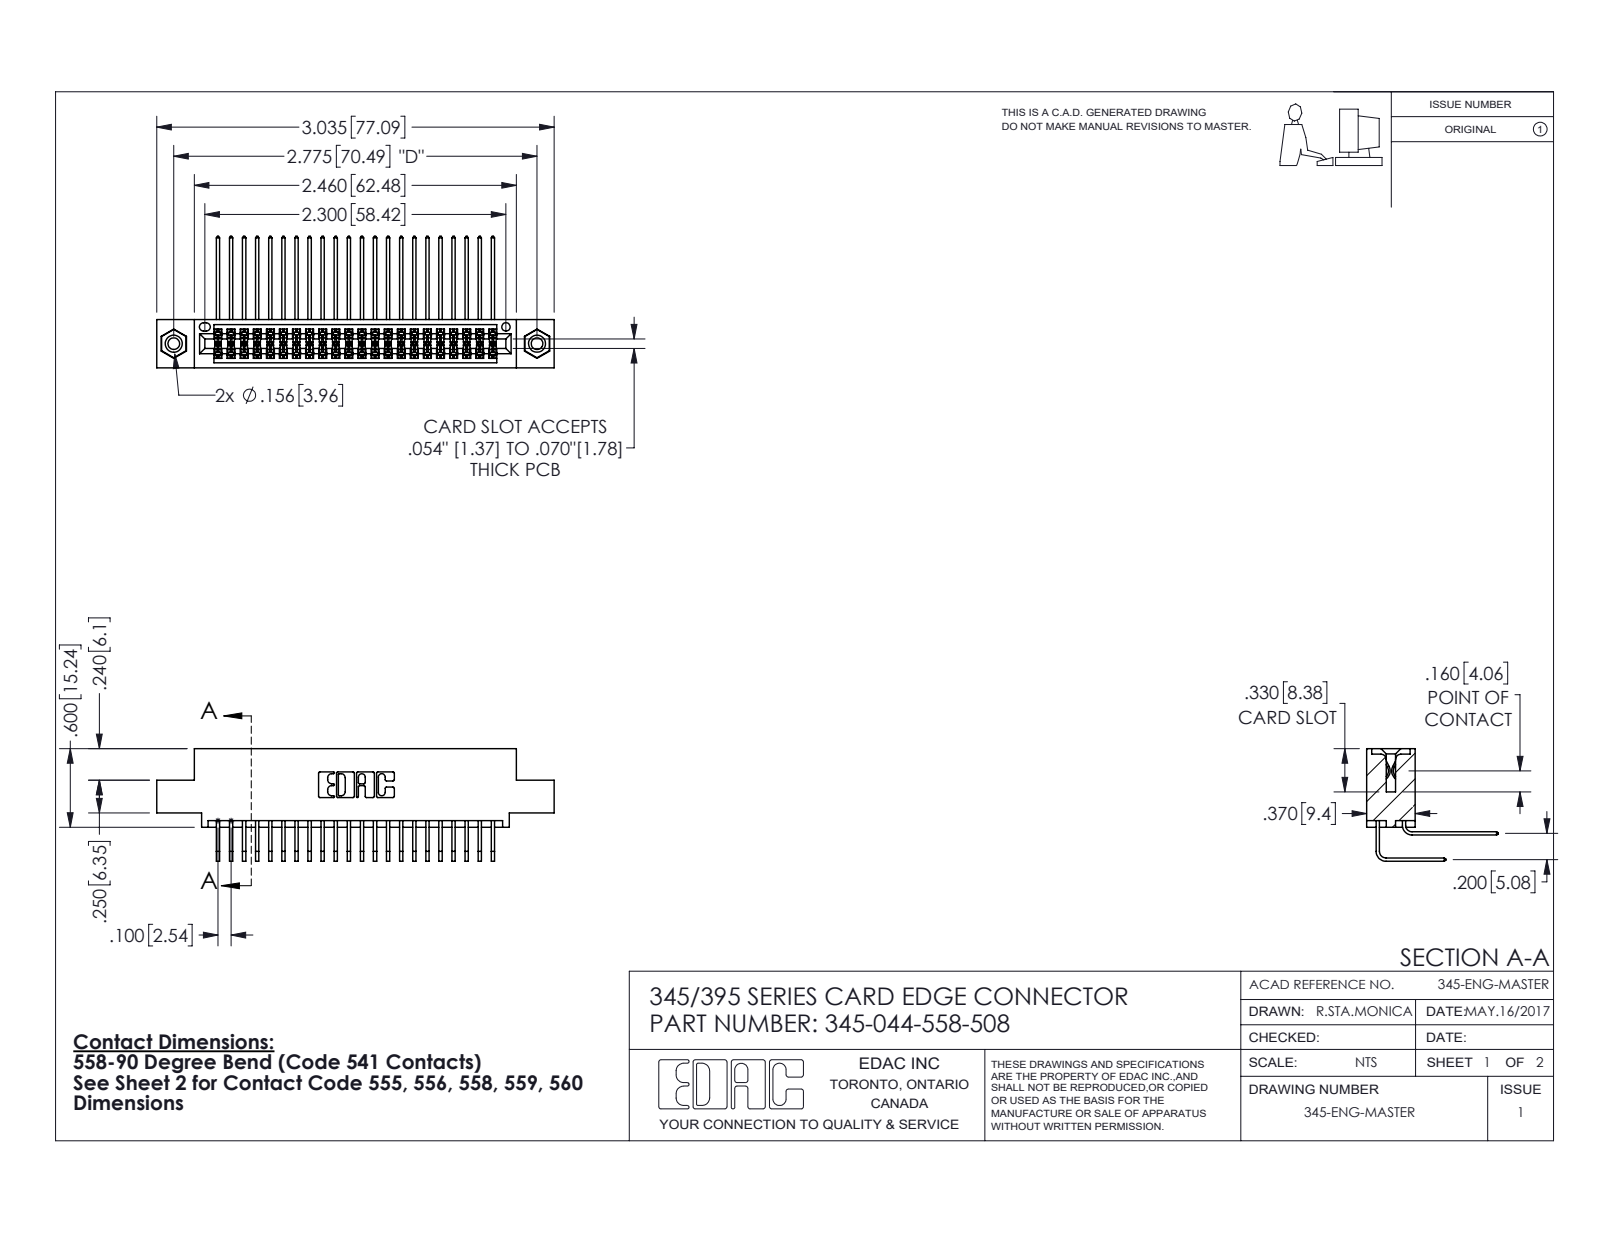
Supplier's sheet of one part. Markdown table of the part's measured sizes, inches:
| quantity | value |
| --- | --- |
| part name | 345-292-001_558 Tail - 2; 345-292-001_558 559 Tail - 1; 345-250-001_345-250-003-102; 345-044-558-508 (+1 more) |
| STEP written by | SolidWorks 2016 (CONFIG_CONTROL_DESIGN) |
| units | inches |
| bodies | 47 solids, 2478 faces (1656 planar, 806 cylindrical, 16 other) |
| overall size | 3.035 × 1.005 × 0.859 |
| volume | 0.456 in³ |
| surface area | 18.54 in² |
| round holes (diameter × count) | 0.089 × 2, 0.125 × 2, 0.156 × 2, 0.064 × 1 |
| round bosses / shafts (diameter × count) | 0.155 × 2 |
| partial cylindrical surfaces (radius × count) | 0.006 × 88, 0.01 × 22, 0.007 × 6, 0.031 × 6, 0.026 × 3, 0.014 × 2, 0.019 × 2, 0.022 × 2 |
| main face-to-face distances | 0.072, 0.298, 0.2, 0.37, 0.098, 0.272, 0.025, 0.225, 0.025, 0.175 |
| hole center spacings | 0.27, 2.541, 2.775 |
